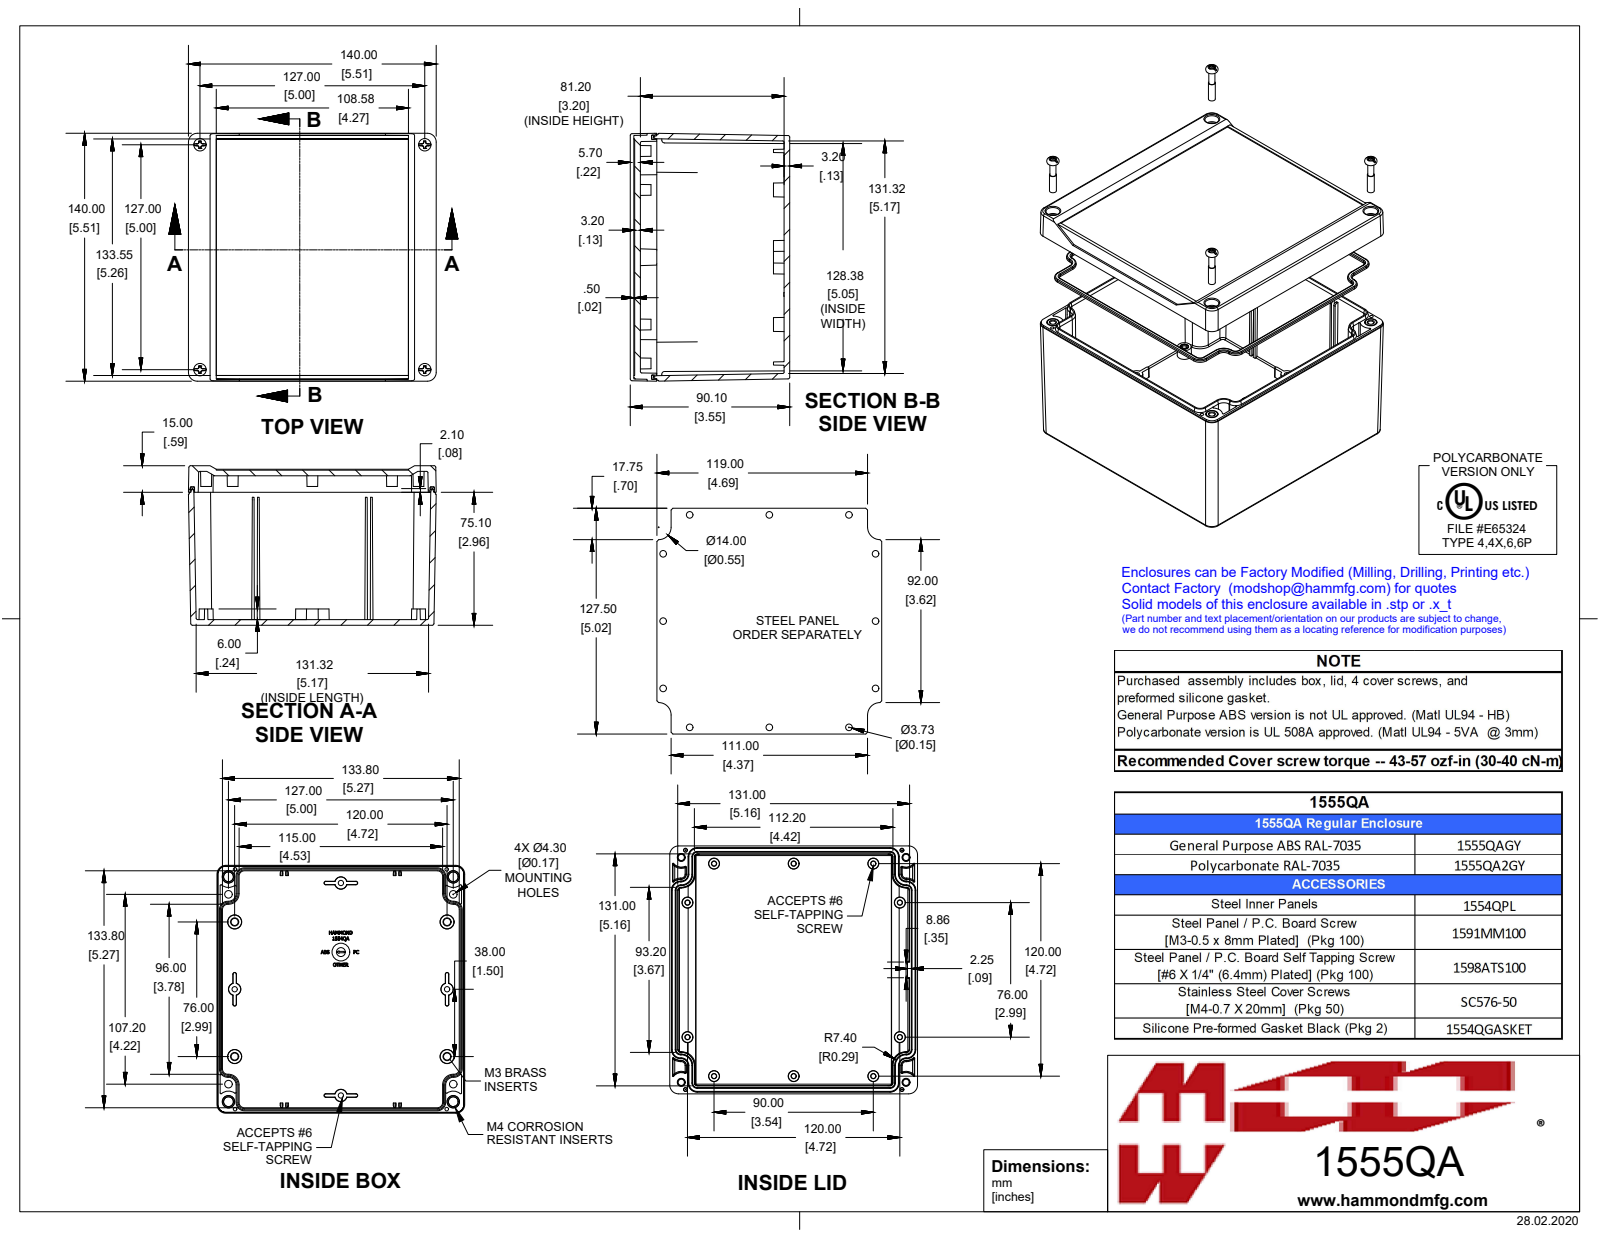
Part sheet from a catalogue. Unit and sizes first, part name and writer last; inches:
Units: inches
Overall size (bounding box): 5.512 × 5.512 × 3.547
Round holes (diameter × count): ⌀0.097 ×4, ⌀0.128 ×4, ⌀0.181 ×4, ⌀0.138 ×3
Round bosses / shafts (diameter × count): ⌀0.25 ×4, ⌀0.218 ×4, ⌀0.21 ×4, ⌀0.19 ×4, ⌀0.154 ×4, ⌀0.153 ×4, ⌀0.15 ×4, ⌀0.135 ×4
Partial cylindrical surfaces — rounded edges, fillets, slot ends (radius × count): R0.02 ×26, R0.012 ×22, R0.039 ×12, R0.031 ×10, R0.104 ×8, R0.197 ×8, R0.199 ×8, R0.118 ×4
Main face-to-face distances: 0.126, 3.323, 0.122, 3.449, 3.197, 5.512, 5.39, 0.098, 5.335, 0.177
Hole centre spacings: 1.013, 3.998, 4.965, 5, 6.294, 2.992, 4.724, 5.592
Volume: 18.06 in³ · Surface area: 314.6 in²
Bodies: 15 solids, 1954 faces (661 planar, 381 cylindrical, 912 other)
Part name (STEP PRODUCT): 1555QA2GY
STEP written by: SolidWorks 2019 (AUTOMOTIVE_DESIGN)
